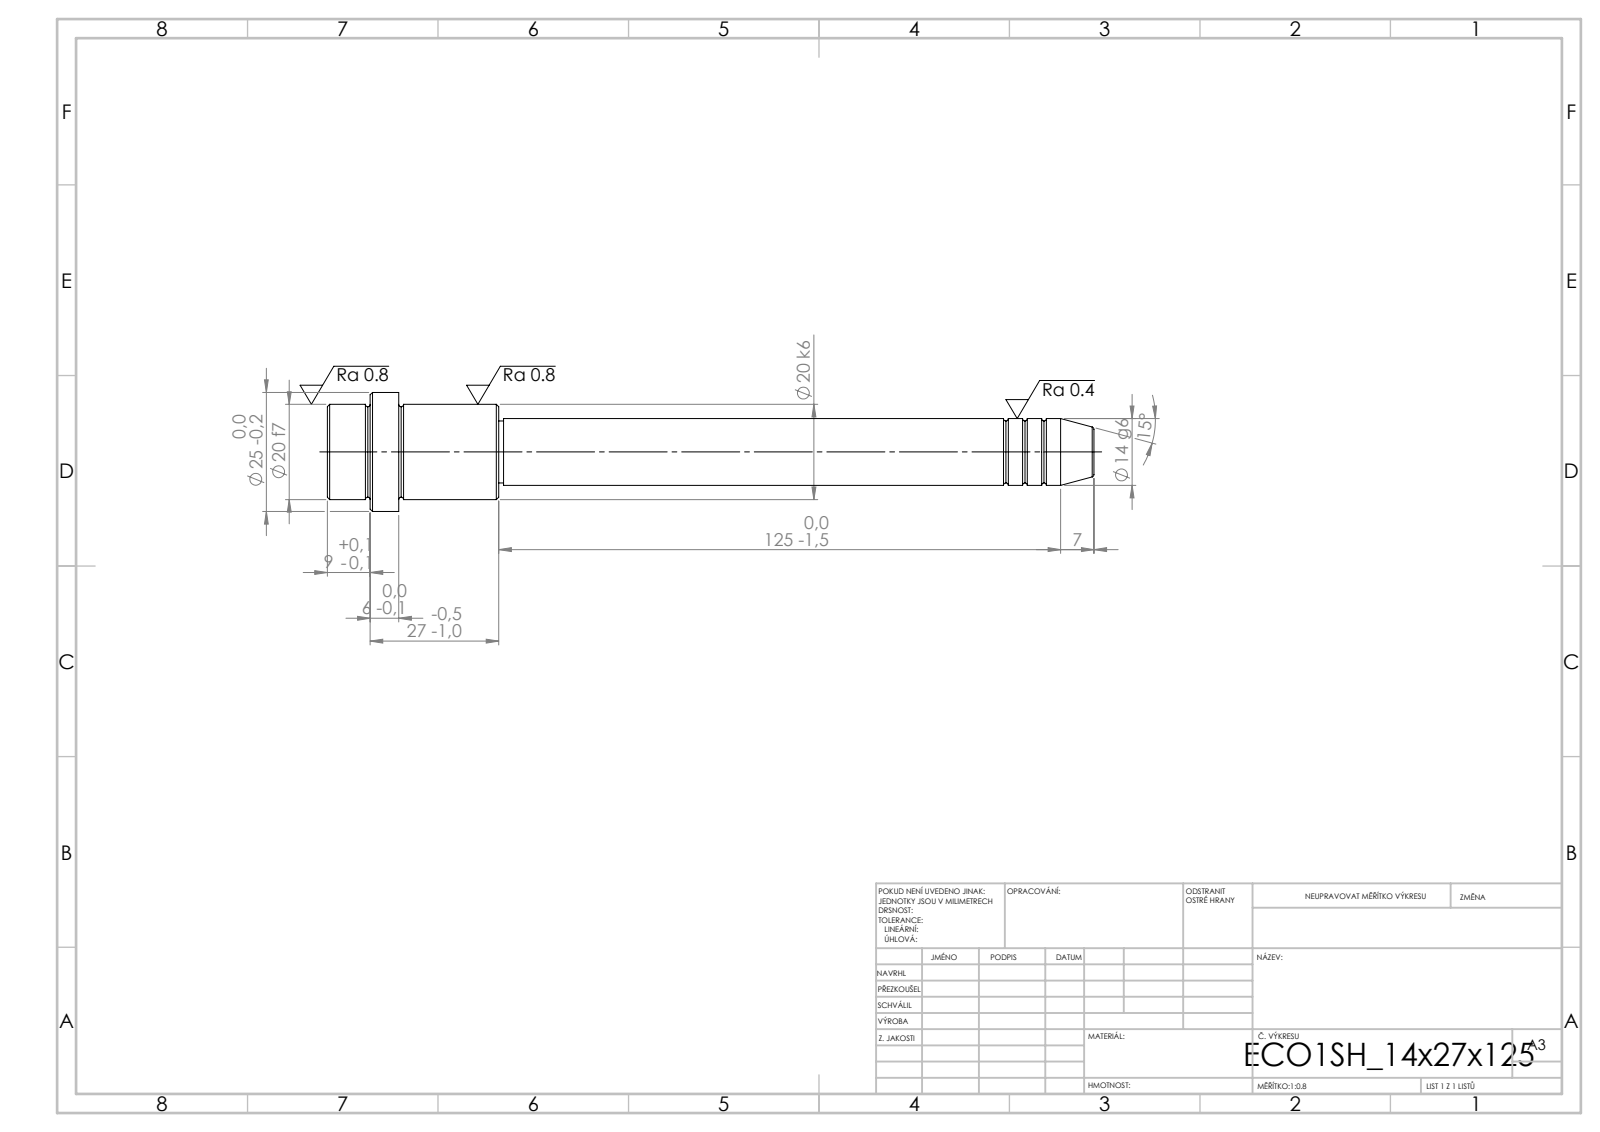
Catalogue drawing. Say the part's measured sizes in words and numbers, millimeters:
Its 3-D file was written by "SolidWorks 2019 (CONFIG_CONTROL_DESIGN)". It is 1 solid with 52 faces: 6 planar, 16 cylindrical and 30 other. Overall it measures 161 by 25 by 25 millimeters. Its volume is 31 204 cubic millimeters and its surface area 8 839 square millimeters. Round bosses or shafts: 1 of diameter 25, 1 of diameter 20, 1 of diameter 14, 1 of diameter 13. The main face-to-face distances are 15, 21, 36, 27, 6, 9, 125, 146, 152, 161.
